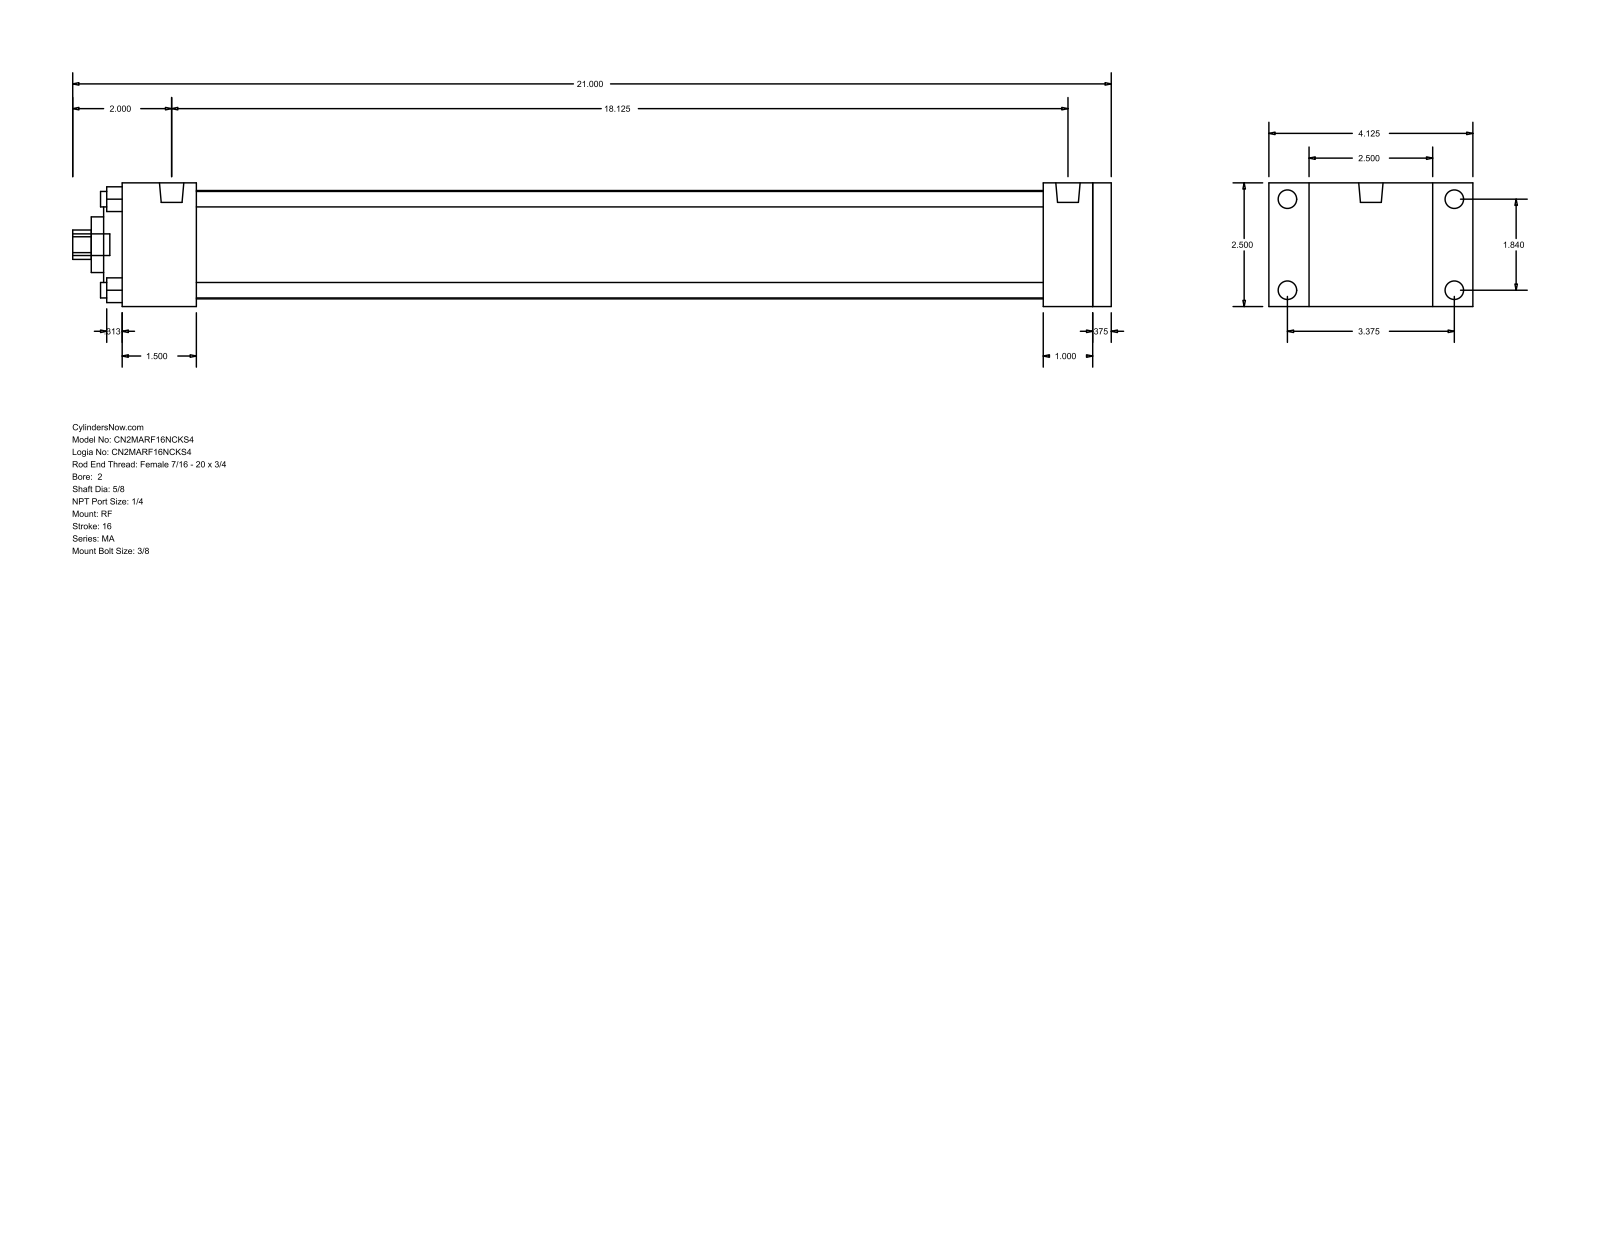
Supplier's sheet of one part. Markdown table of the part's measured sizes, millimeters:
| quantity | value |
| --- | --- |
| part name | MA_RF__0200_0.625 |
| STEP written by | GSSL Pune (CONFIG_CONTROL_DESIGN) |
| units | millimeters |
| bodies | 0 solids, 94 faces (65 planar, 29 cylindrical, 0 other) |
| overall size | 533.4 × 104.78 × 63.5 |
| round holes (diameter × count) | 7.94 × 4, 15.88 × 1, 28.57 × 1, 50.8 × 1, 55.63 × 1 |
| round bosses / shafts (diameter × count) | 9.53 × 4, 7.94 × 4, 12.49 × 2, 11.11 × 1 |
| partial cylindrical surfaces (radius × count) | 7.54 × 1 |
| main face-to-face distances | 63.5, 9.52, 508, 25.4, 38.1, 498.48, 460.38, 469.9, 473.08, 434.98 |
| hole center spacings | 33.05, 46.74, 66.1 |
